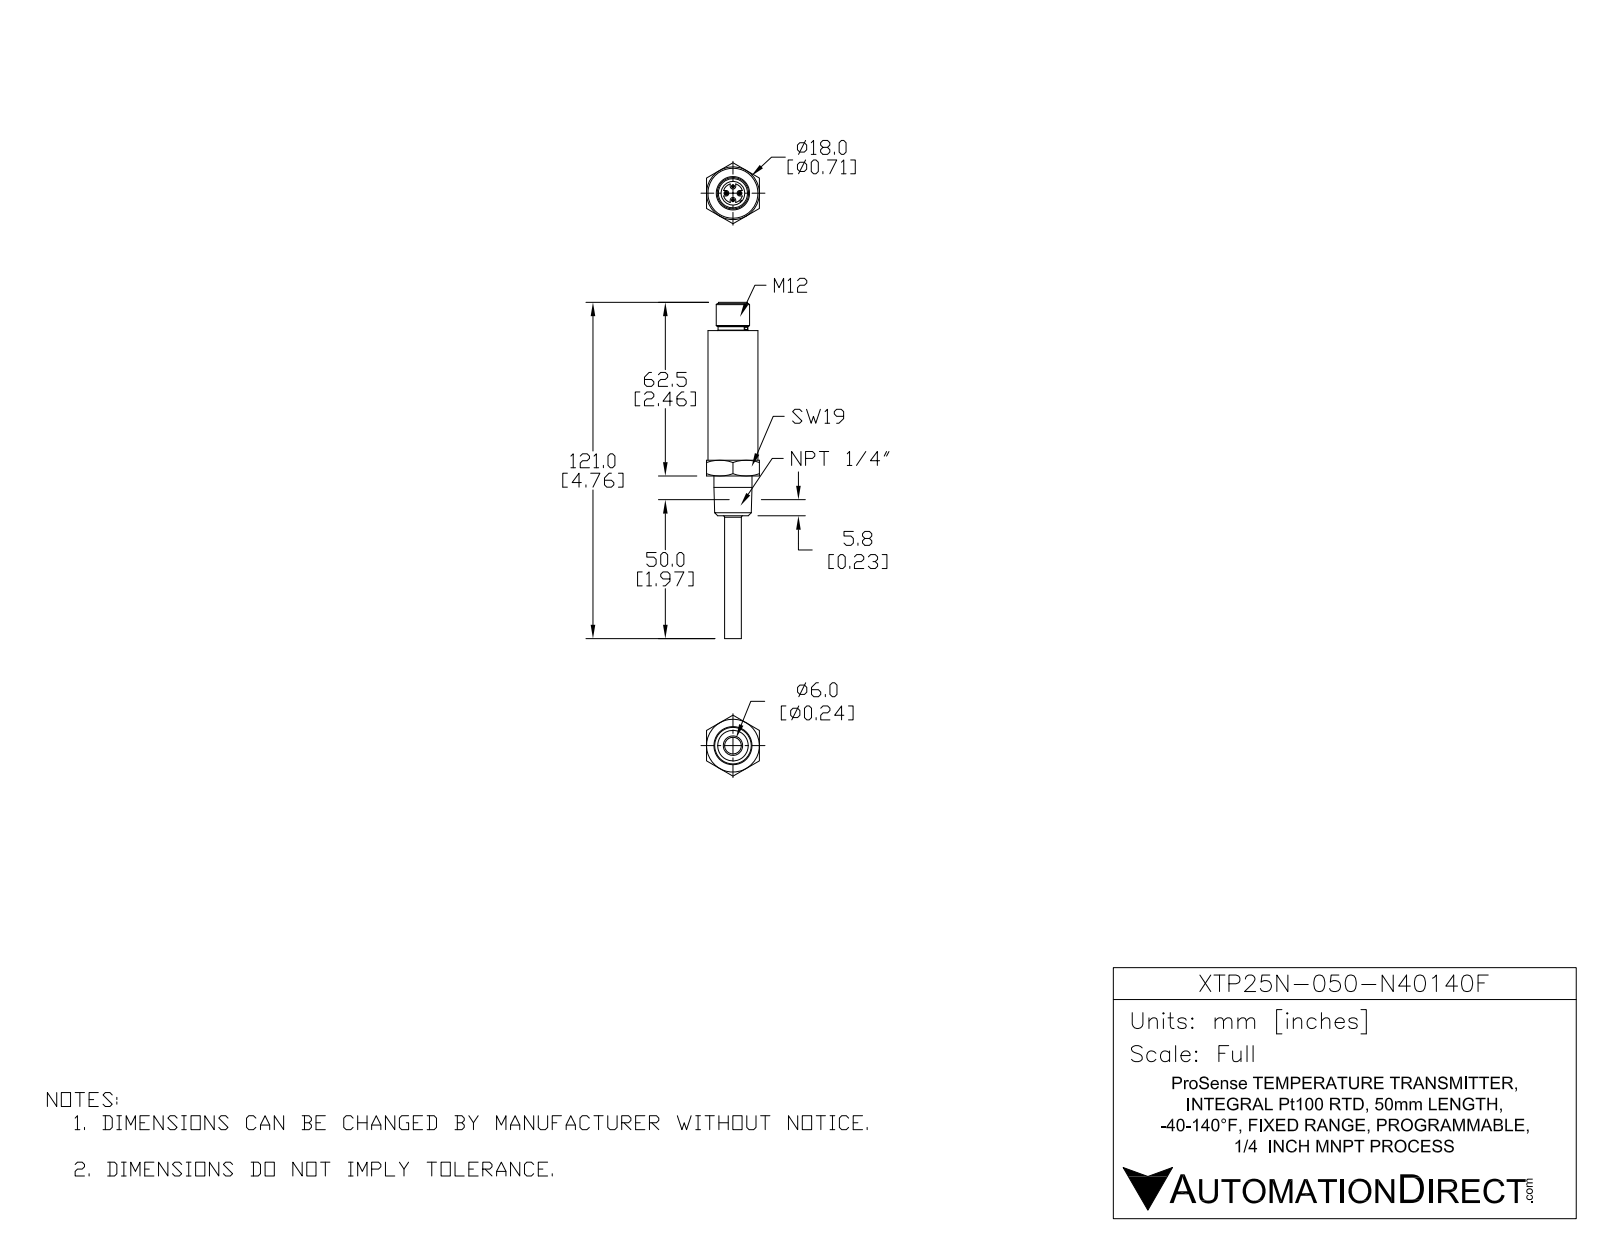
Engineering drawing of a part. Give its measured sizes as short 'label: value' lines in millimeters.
name: XTP25N-050-N40140F
written by: SolidWorks 2015 (AUTOMOTIVE_DESIGN)
unit: mm
bodies: 1 solid, 117 faces (43 planar, 34 cylindrical, 40 other)
size: 121 × 21.94 × 19
volume: 17 233 mm³; area: 6 004 mm²
holes: 1× ⌀4, 1× ⌀8.5
bosses: 4× ⌀1.02, 1× ⌀18, 1× ⌀13.72, 1× ⌀12, 1× ⌀10.7, 1× ⌀10.5, 1× ⌀6
rounds: 4× R1, 1× R3.5, 1× R4.25
face distances: 19, 52.3, 14.3, 66.6, 20, 5.7, 46.6, 76.8, 62.5, 56.8
